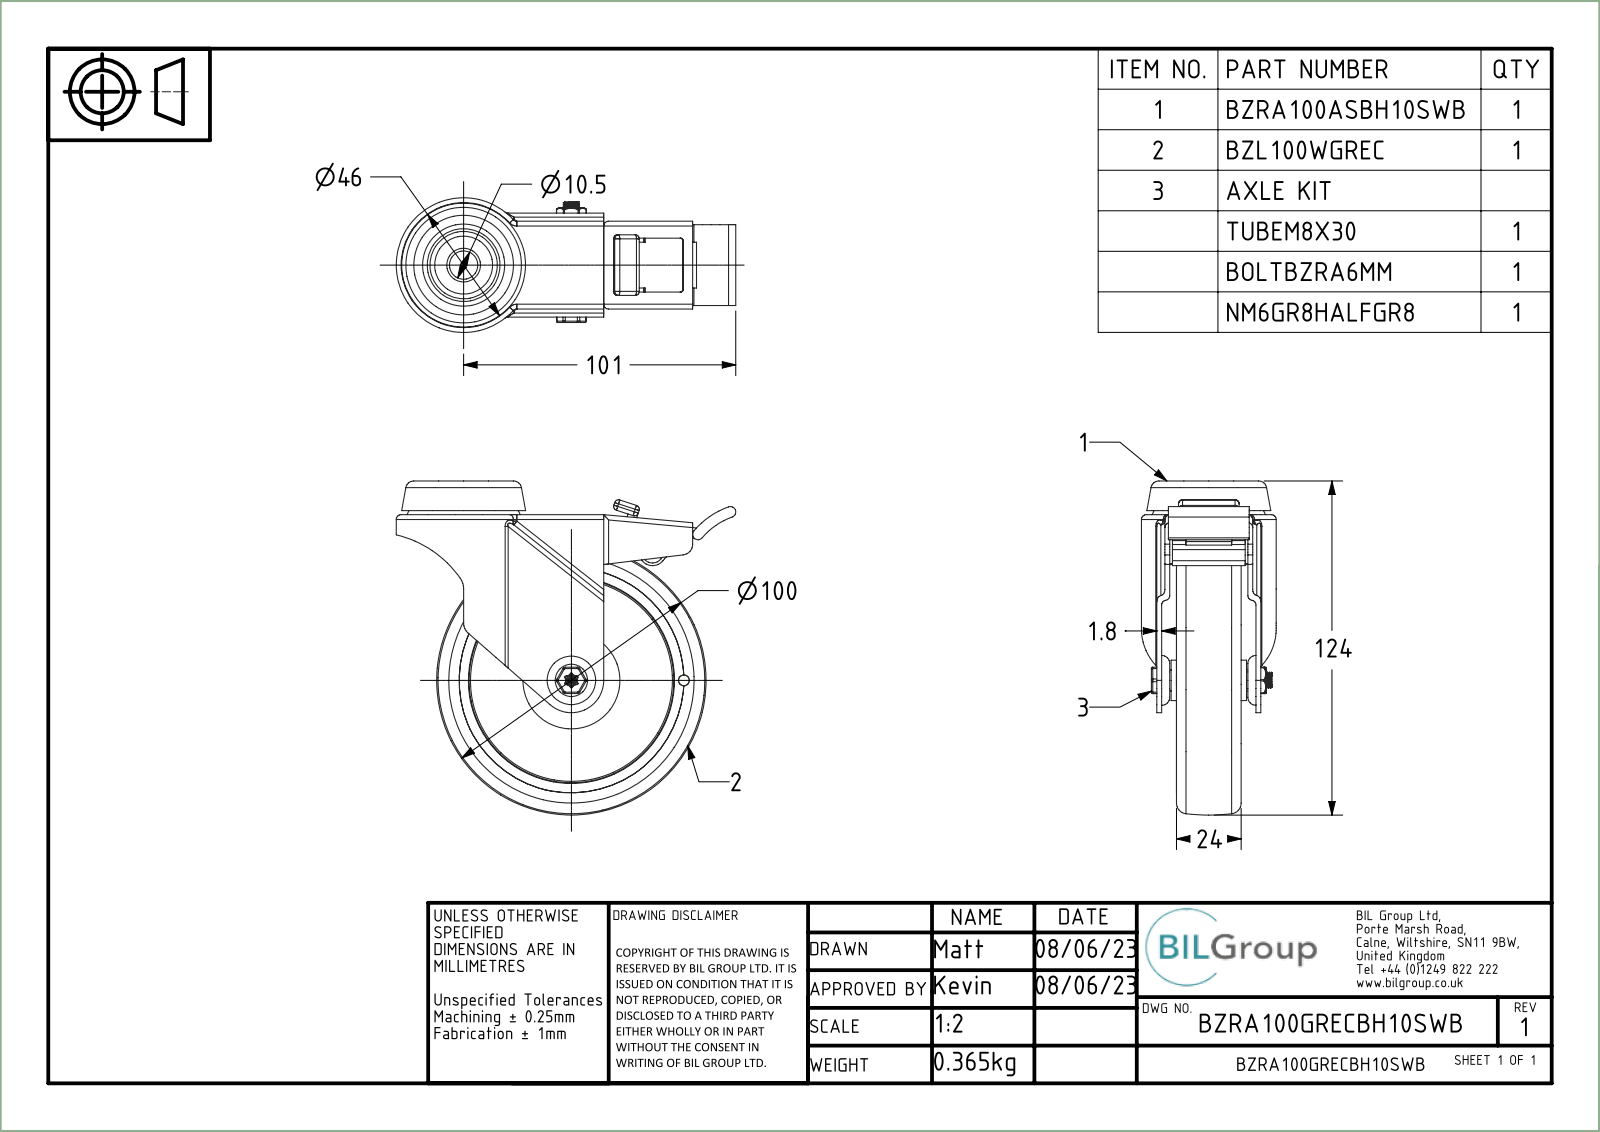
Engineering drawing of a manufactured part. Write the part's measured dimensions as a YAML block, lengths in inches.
part_name: "BZRA100ASBH10SWB; ZINC PLATED PRESSED STEEL HEAD; ZINC PLATED PRESSED STEEL FORKS; ZINC PLATED PRESSED STEEL BRAKE (+8 more)"
step_written_by: "Spatial InterOp 3D (CONFIG_CONTROL_DESIGN)"
units: inches
bodies: {solids: 11, faces: 640, planar: 204, cylindrical: 260, other: 176}
overall_size: [4.961, 4.882, 1.969]
volume: 8.6
surface_area: 132.4
round_holes:
  - {diameter: 0.157, count: 1}
  - {diameter: 0.236, count: 1}
  - {diameter: 0.248, count: 1}
  - {diameter: 0.252, count: 1}
  - {diameter: 0.319, count: 1}
  - {diameter: 0.327, count: 1}
  - {diameter: 0.413, count: 1}
  - {diameter: 0.416, count: 1}
  - {diameter: 1.181, count: 1}
  - {diameter: 3.287, count: 1}
round_bosses_or_shafts:
  - {diameter: 1.535, count: 1}
  - {diameter: 0.709, count: 1}
  - {diameter: 0.591, count: 1}
  - {diameter: 0.581, count: 1}
  - {diameter: 0.315, count: 1}
  - {diameter: 0.313, count: 1}
  - {diameter: 0.197, count: 1}
partial_cylinders:
  - {radius: 0.071, count: 27}
  - {radius: 0.039, count: 22}
  - {radius: 0.02, count: 13}
  - {radius: 0.059, count: 12}
  - {radius: 0.016, count: 6}
  - {radius: 0.035, count: 4}
  - {radius: 0.079, count: 4}
  - {radius: 0.197, count: 2}
face_to_face_distances: [0.071, 1.331, 0.157, 0.118, 0.394, 0.551, 0.492, 0.189, 1.232, 0.098]
hole_center_spacings: [1.644]
